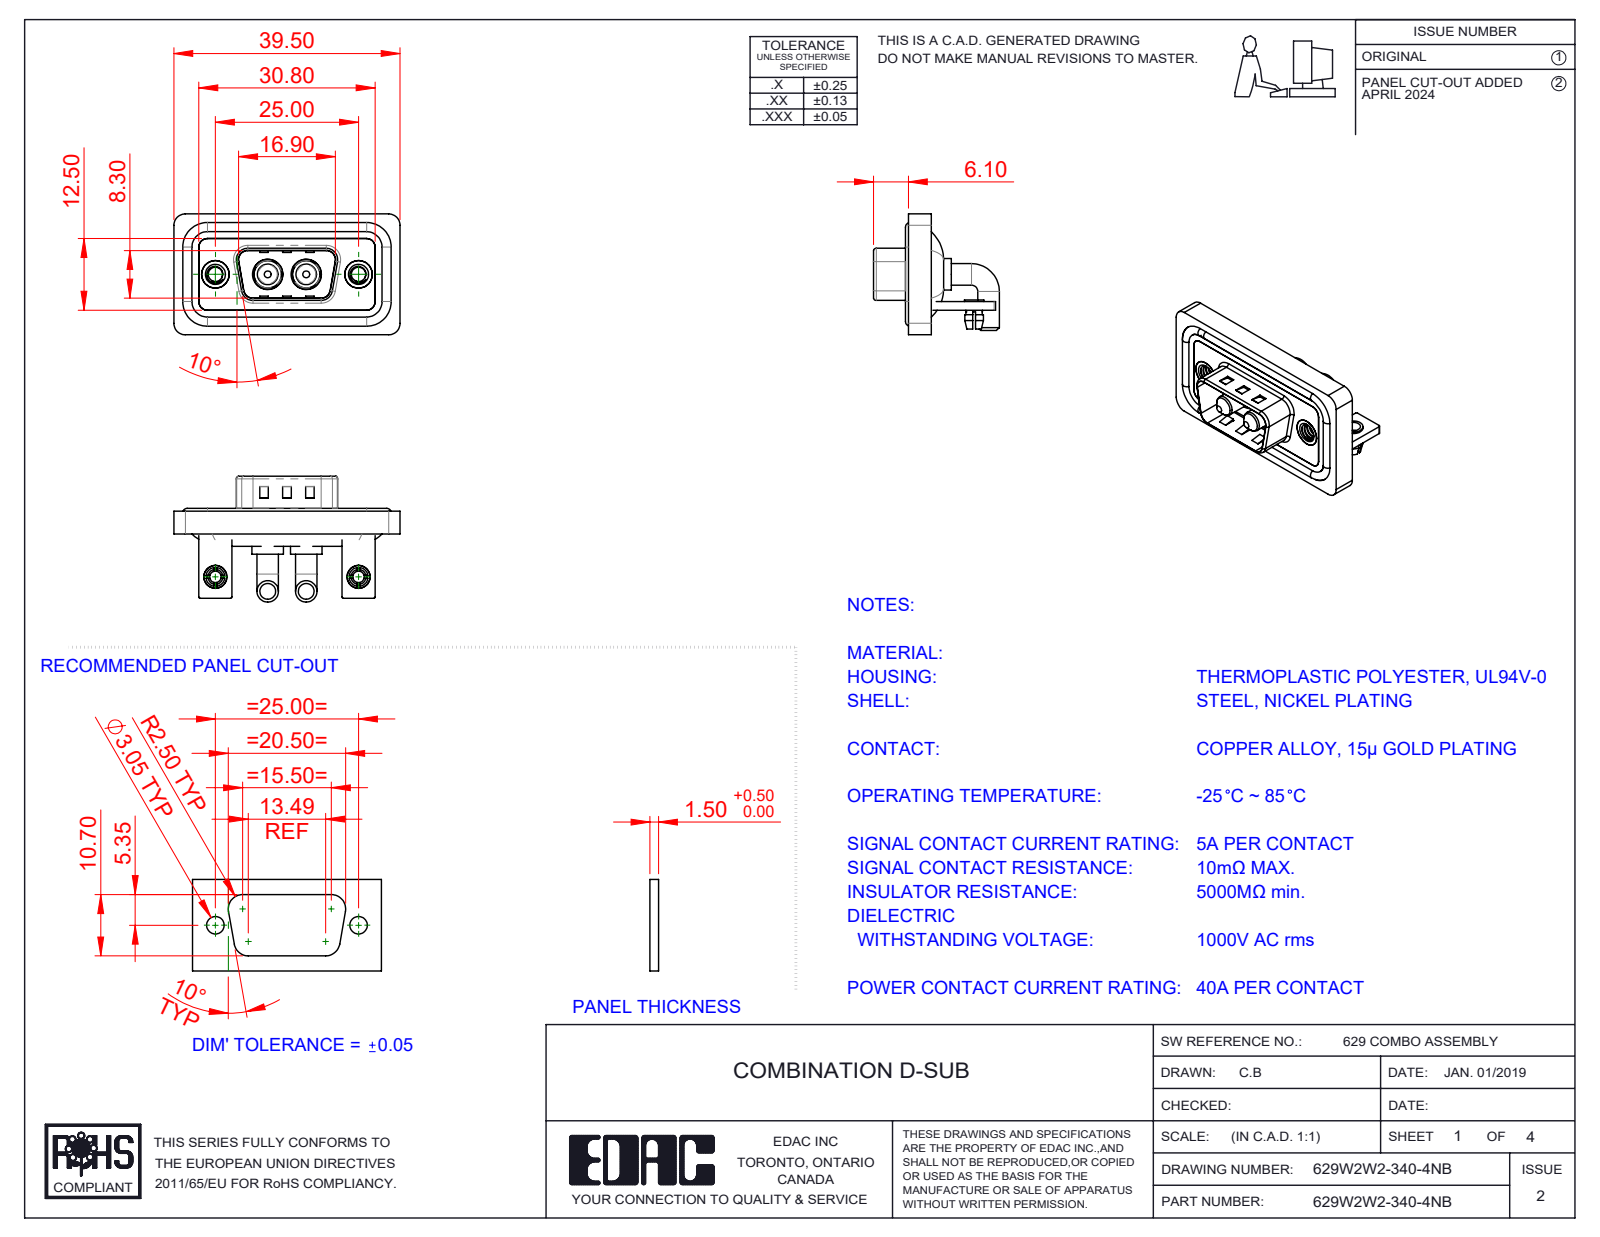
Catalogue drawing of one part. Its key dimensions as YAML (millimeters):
part_name: "629Combo Waterproof Housing_09 Contacts; 629Combo Shell Rear_09 Contacts; 629W2W2-340-4NB; 629Combo Board Lock (+5 more)"
step_written_by: "SolidWorks 2023 (CONFIG_CONTROL_DESIGN)"
units: millimeters
bodies: {solids: 15, faces: 627, planar: 233, cylindrical: 272, other: 122}
overall_size: [39.5, 21.98, 21.1]
volume: 5038
surface_area: 8054
round_holes:
  - {diameter: 2.5, count: 4}
  - {diameter: 2, count: 2}
  - {diameter: 3.2, count: 2}
  - {diameter: 4, count: 2}
  - {diameter: 4.8, count: 2}
  - {diameter: 4.85, count: 2}
  - {diameter: 5, count: 2}
  - {diameter: 5.3, count: 2}
round_bosses_or_shafts:
  - {diameter: 3.75, count: 4}
  - {diameter: 1.6, count: 4}
  - {diameter: 5.5, count: 2}
  - {diameter: 5.2, count: 2}
  - {diameter: 4.9, count: 2}
  - {diameter: 4.75, count: 2}
  - {diameter: 4, count: 2}
  - {diameter: 3.6, count: 2}
partial_cylinders:
  - {radius: 2, count: 19}
  - {radius: 1.5, count: 18}
  - {radius: 0.25, count: 16}
  - {radius: 0.5, count: 9}
  - {radius: 1.6, count: 8}
  - {radius: 0.6, count: 4}
  - {radius: 0.65, count: 4}
  - {radius: 0.9, count: 4}
face_to_face_distances: [0.4, 1.5, 2.9, 0.8, 1.1, 1.2, 2.1, 1.6, 3.7, 2.5]
hole_center_spacings: [9.14, 15.86, 25, 6.72]
